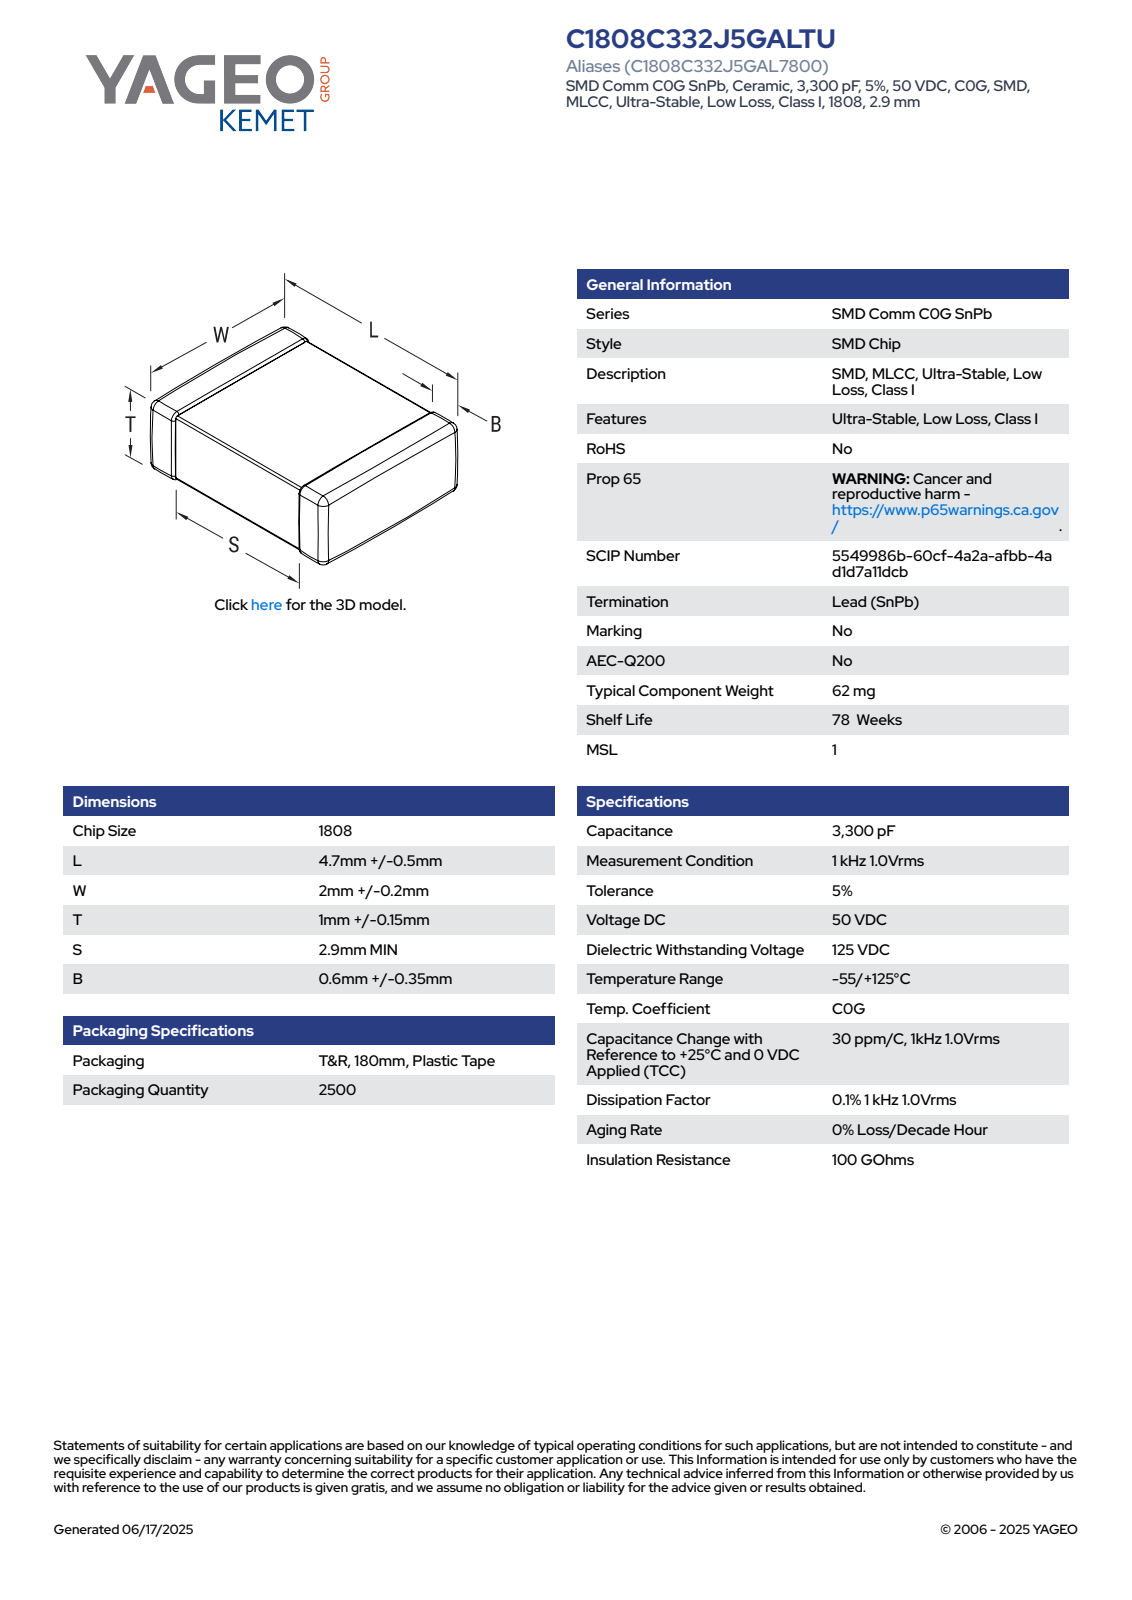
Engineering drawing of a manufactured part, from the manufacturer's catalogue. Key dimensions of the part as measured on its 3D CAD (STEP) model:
Part name (STEP PRODUCT): CCS_CCSTDNOS_1808_L5.2W2.2T1.15B0.95
STEP written by: SolidWorks 2014 (AUTOMOTIVE_DESIGN)
Units: millimetres
Bodies: 4 solids, 129 faces (71 planar, 42 cylindrical, 16 other)
Overall size (bounding box): 5.2 × 2.2 × 1.15
Volume: 12 mm³ · Surface area: 39 mm²
Main face-to-face distances: 1.1, 1.05, 2.15, 1.15, 2.1, 5.2, 2.2, 1.11, 1.06, 0.89
